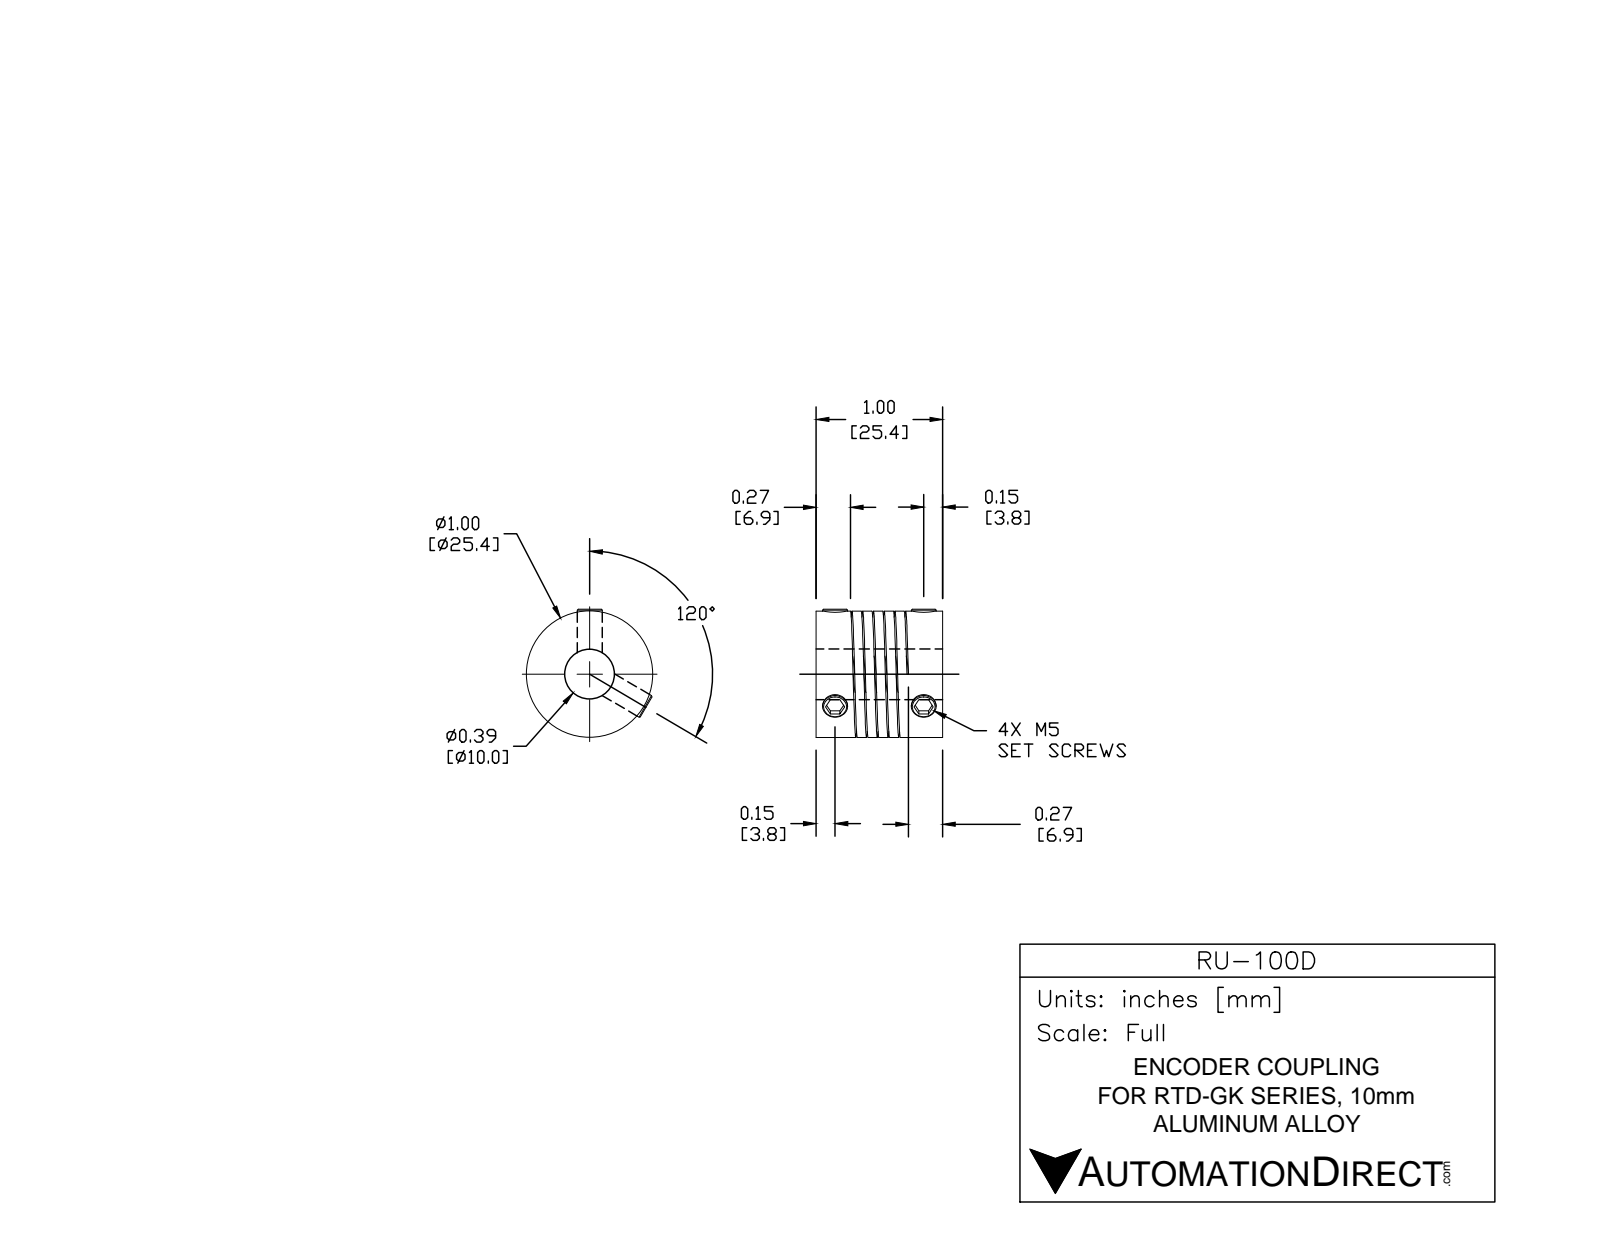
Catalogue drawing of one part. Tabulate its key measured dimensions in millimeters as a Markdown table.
| quantity | value |
| --- | --- |
| part name | RU-100D |
| STEP written by | SolidWorks 2016 (AUTOMOTIVE_DESIGN) |
| units | millimeters |
| bodies | 1 solid, 142 faces (58 planar, 46 cylindrical, 38 other) |
| overall size | 25.4 × 25.4 × 25.4 |
| volume | 9 379 mm³ |
| surface area | 6 909 mm² |
| round holes (diameter × count) | 2.5 × 4, 5 × 4, 10 × 1, 12 × 1 |
| round bosses / shafts (diameter × count) | 25.4 × 1 |
| main face-to-face distances | 25.4, 6.6, 18.8, 12.2, 15.36, 15.46, 15.47, 1.5 |
| hole center spacings | 17.8 |
